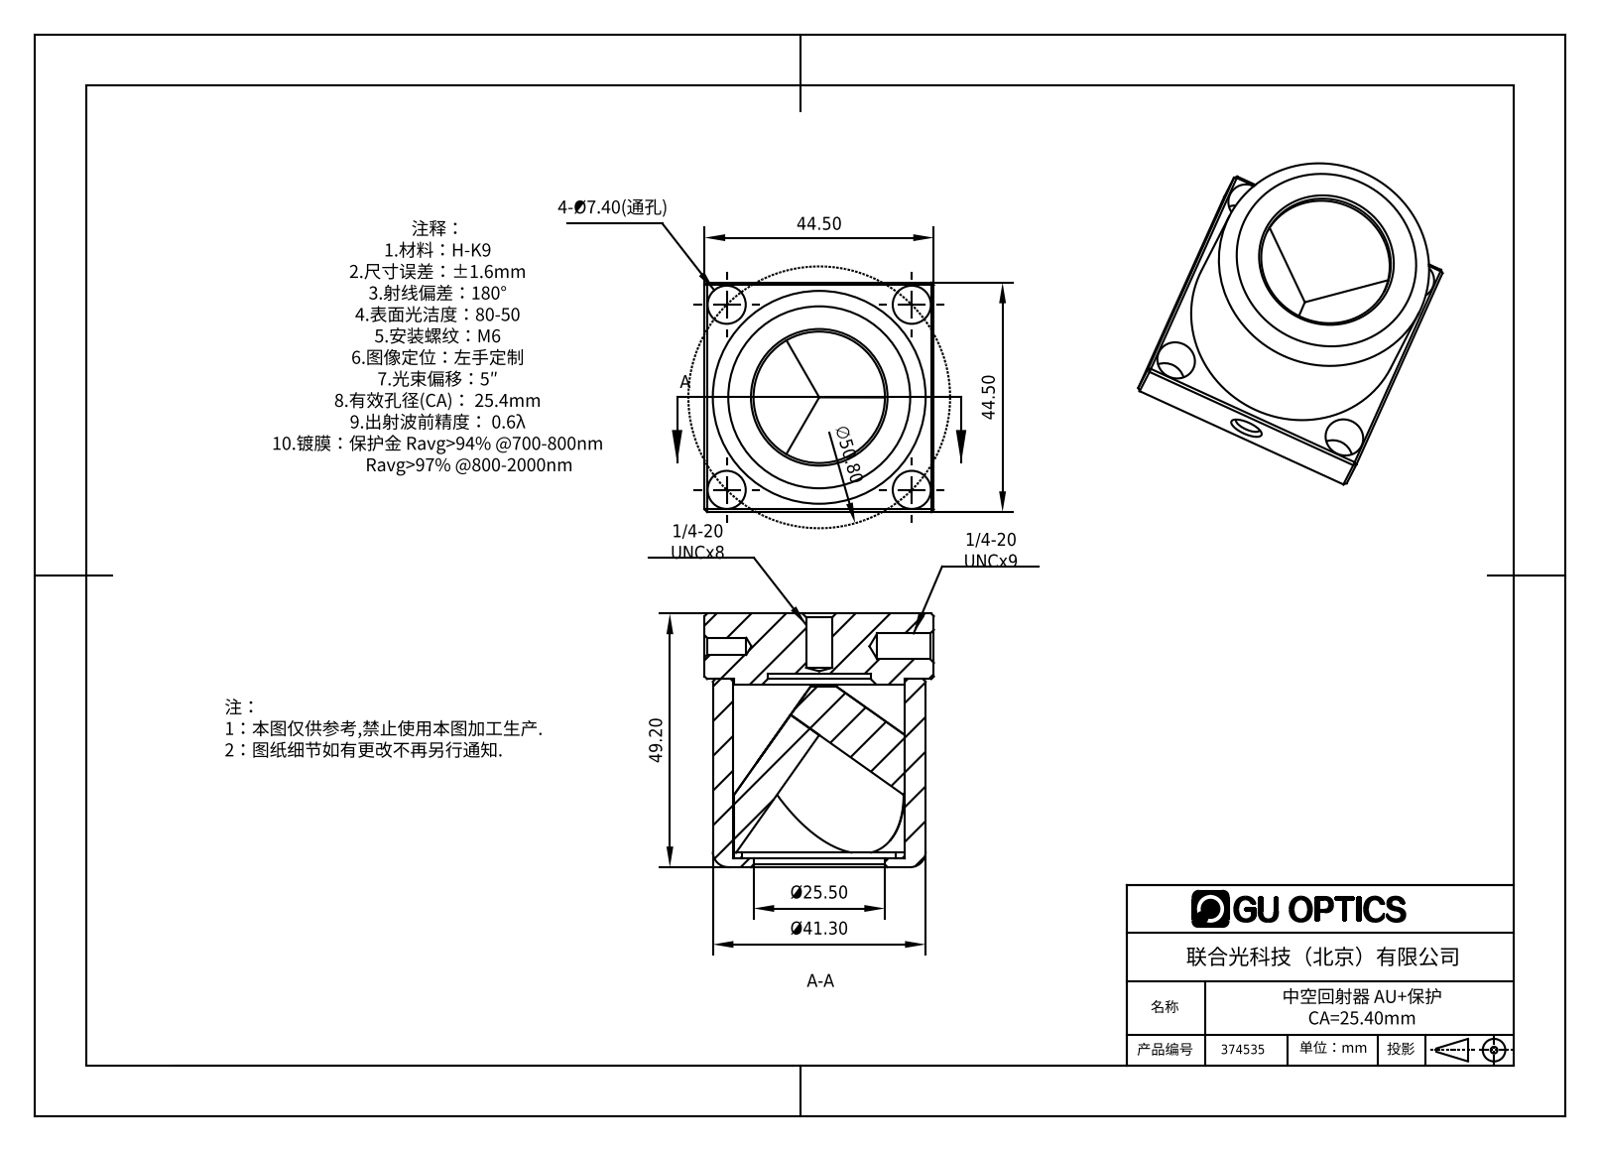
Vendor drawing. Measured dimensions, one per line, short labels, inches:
name: 374528
written by: SolidWorks 2016 (AUTOMOTIVE_DESIGN)
unit: in
bodies: 10 solids, 259 faces (113 planar, 74 cylindrical, 72 other)
size: 1.937 × 1.752 × 1.752
volume: 3.023 in³; area: 38.01 in²
holes: 4× ⌀0.081, 4× ⌀0.11, 4× ⌀0.189, 4× ⌀0.291, 2× ⌀0.201, 1× ⌀0.13, 1× ⌀0.197, 1× ⌀0.787, 1× ⌀1.004, 1× ⌀1.173, 1× ⌀1.311
bosses: 4× ⌀0.177, 4× ⌀0.098, 1× ⌀1.626, 1× ⌀1.307, 1× ⌀1.299
face distances: 0.268, 0.5, 0.039, 1.752, 1.366, 1.327, 1.866, 0.539, 0.071, 1.398
hole spacings: 1.038, 1.239, 1.243, 0.263, 0.269, 0.731, 0.737, 1
